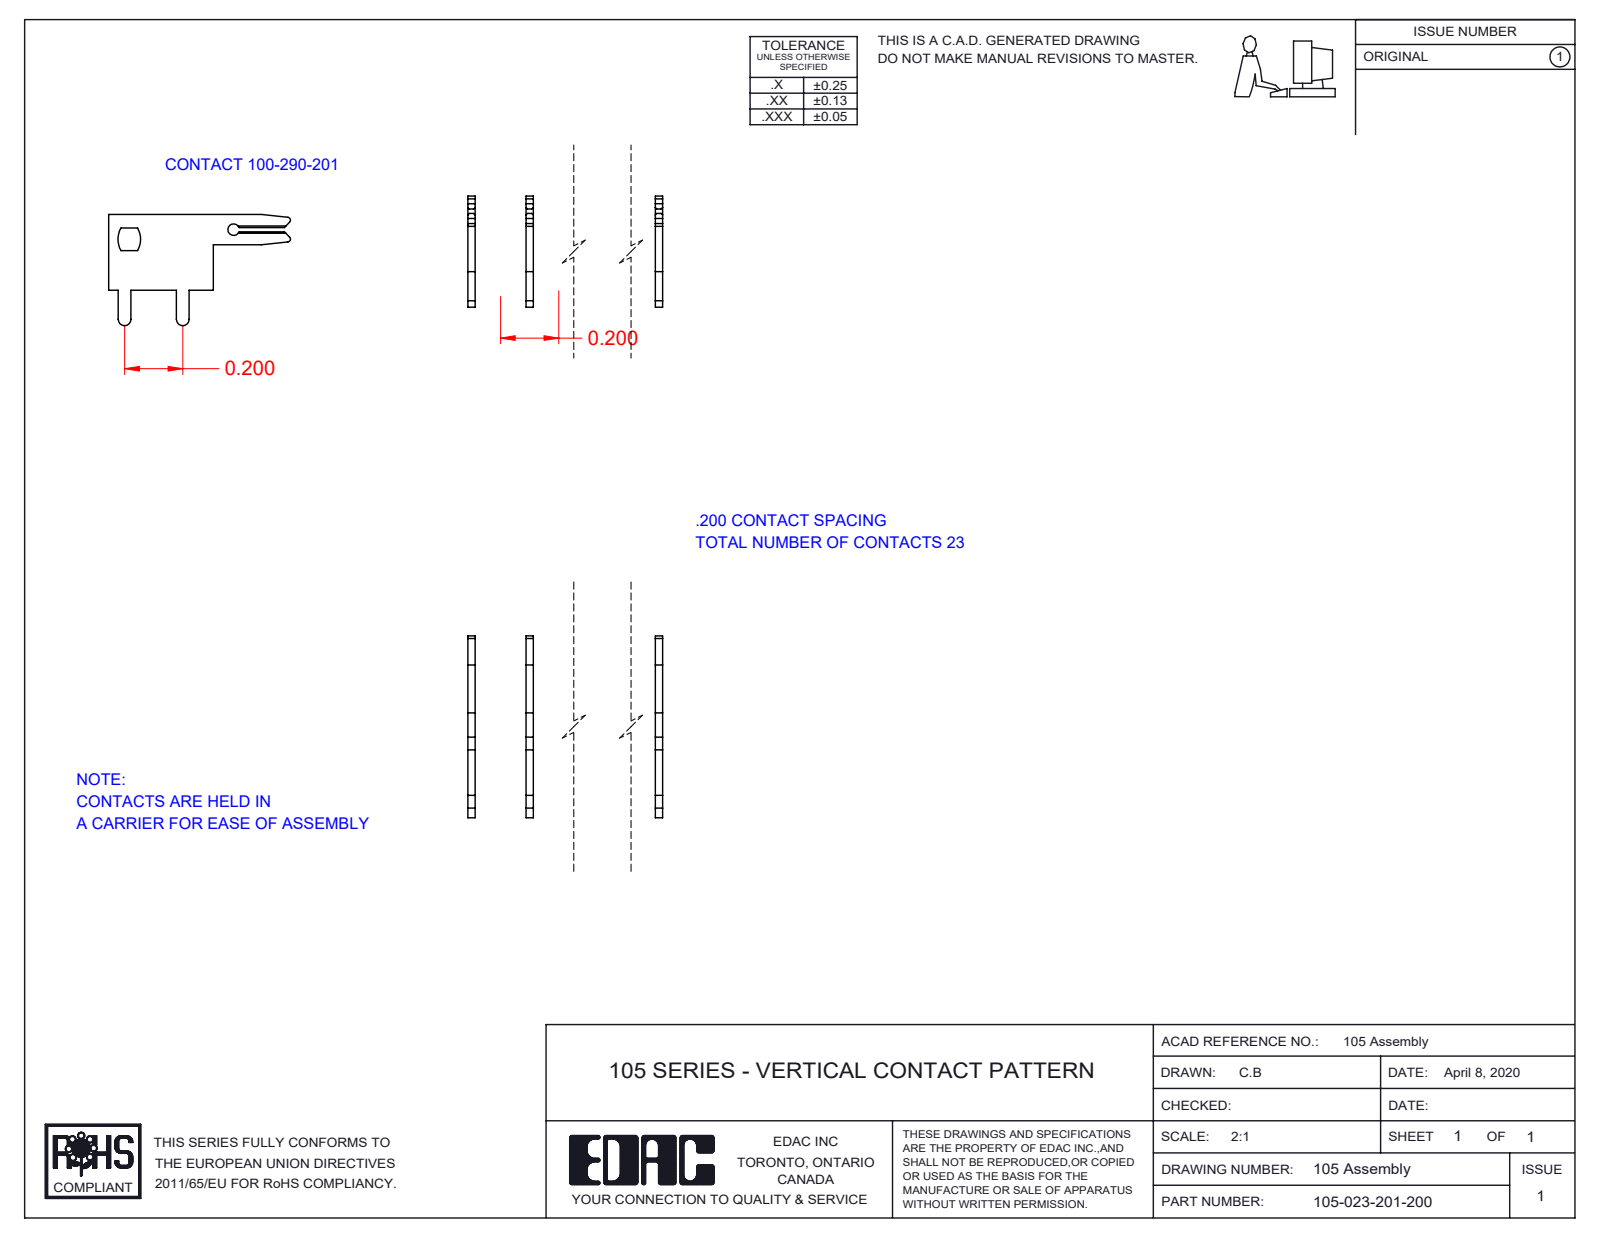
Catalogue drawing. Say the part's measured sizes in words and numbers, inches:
The part is named "105-023-201-200; 100-290-001_100-290-201". Its 3-D file was written by "SolidWorks 2016 (CONFIG_CONTROL_DESIGN)". It is 23 solids with 805 faces: 575 planar, 230 cylindrical and 0 other. Overall it measures 4.425 by 0.625 by 0.382 inches. Its volume is 0.069 cubic inches and its surface area 7.164 square inches. Round holes: 1 of diameter 0.04. Partial cylindrical surfaces (rounded edges, fillets, slot ends): 2 of radius 0.01, 2 of radius 0.022, 2 of radius 0.078. The main face-to-face distances are 0.2, 0.4, 0.6, 0.8, 1, 1.2, 1.4, 1.6, 1.8, 2.
